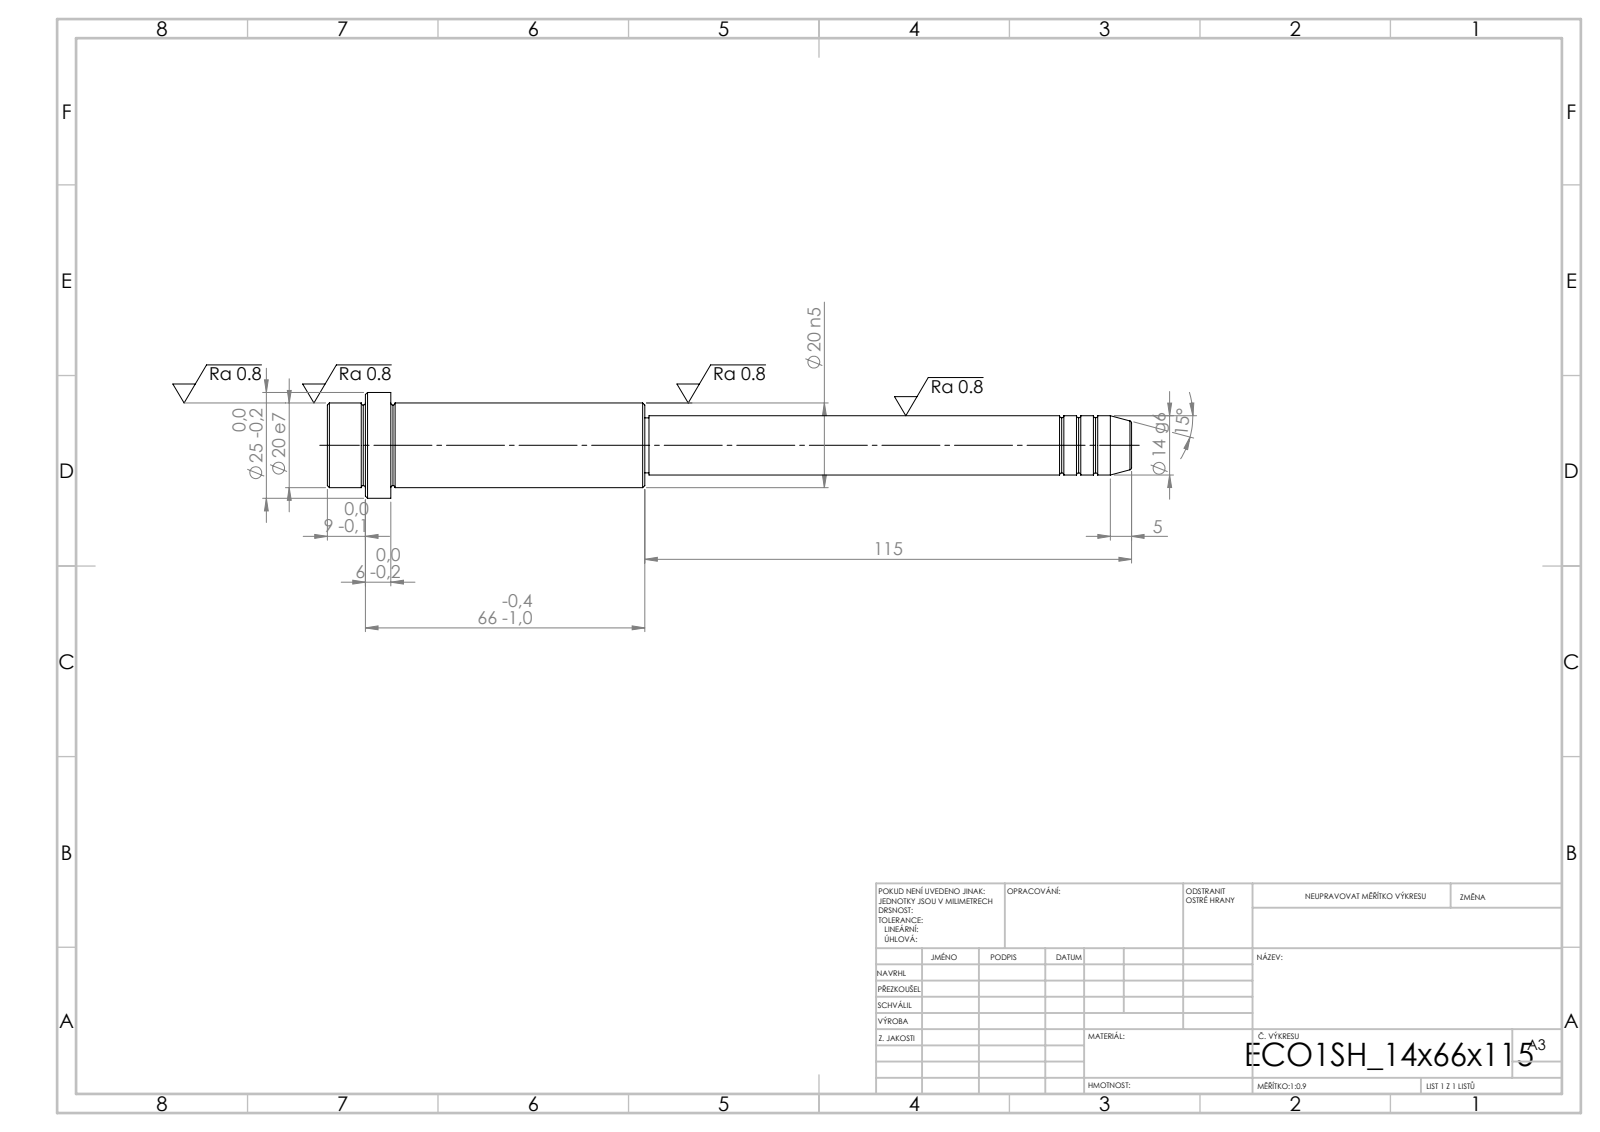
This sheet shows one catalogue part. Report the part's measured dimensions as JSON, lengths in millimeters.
{"step_written_by": "SolidWorks 2019 (CONFIG_CONTROL_DESIGN)", "units": "millimeters", "bodies": {"solids": 1, "faces": 52, "planar": 6, "cylindrical": 16, "other": 30}, "overall_size": [190, 25, 25], "volume_mm3": 42041, "surface_area_mm2": 10885, "round_bosses_or_shafts": [[25, 1], [20, 1], [14, 1], [13, 1]], "face_to_face_distances": [15, 60, 75, 66, 6, 9, 115, 175, 181, 190]}
